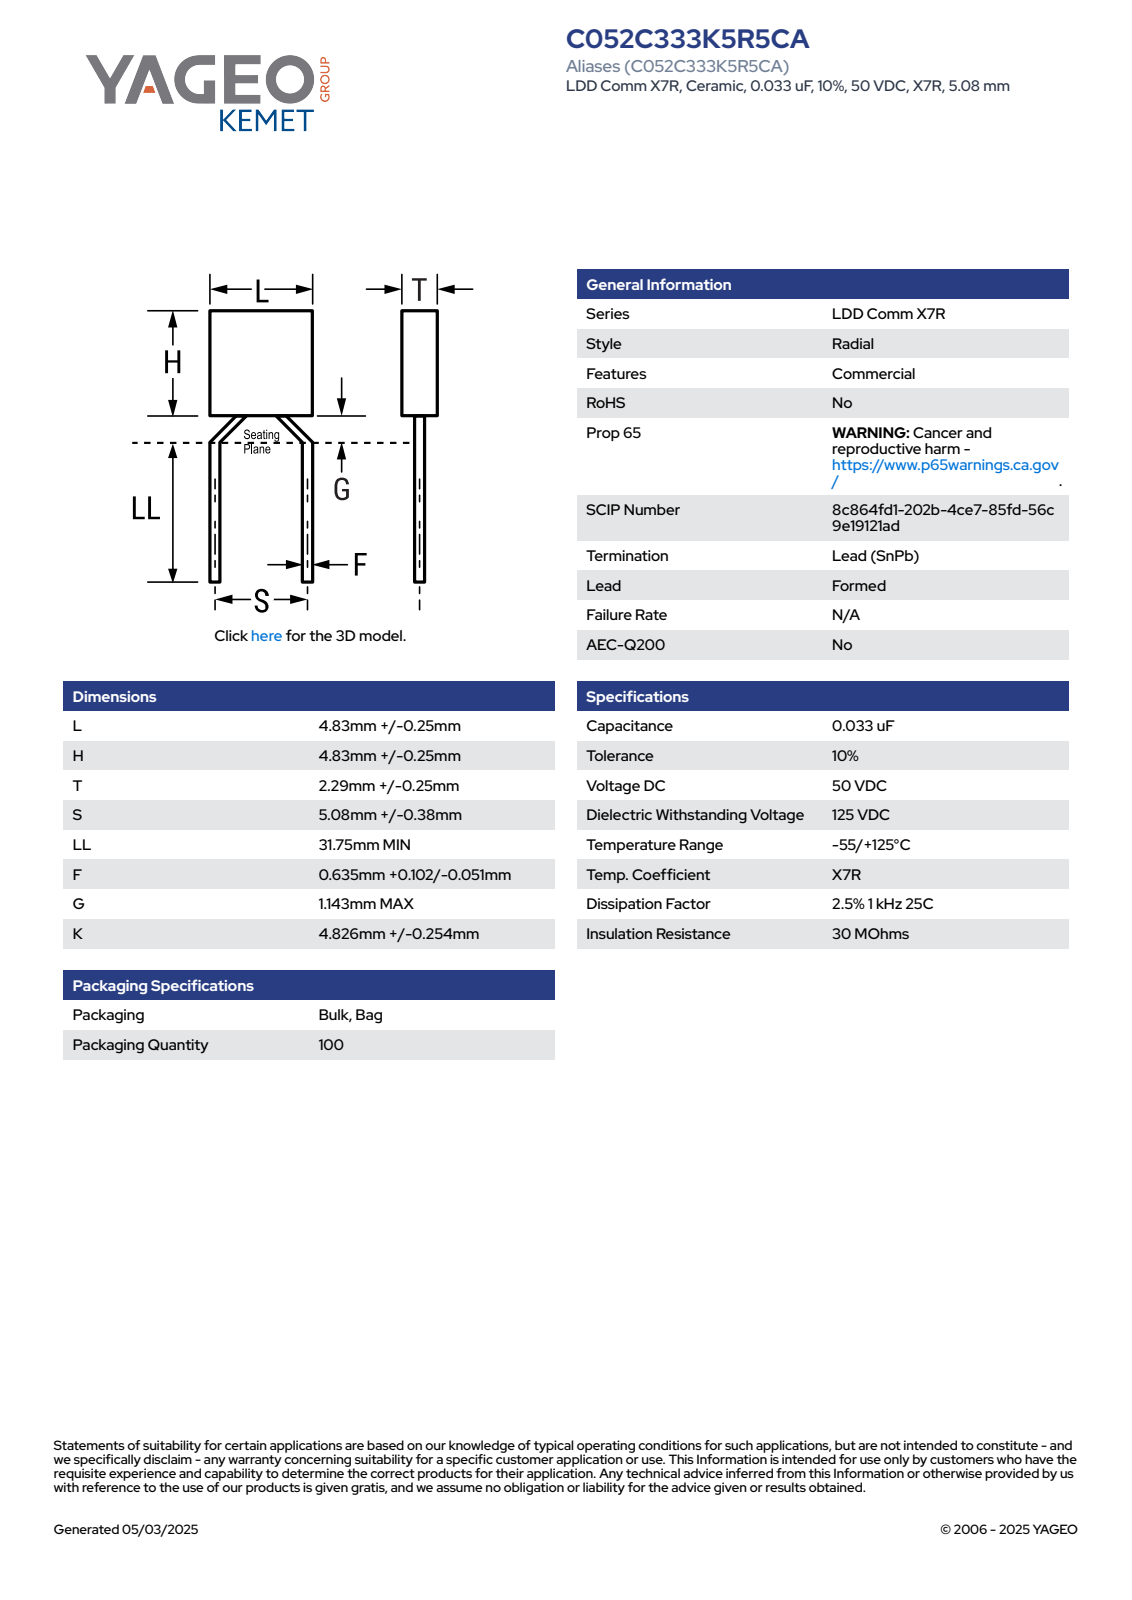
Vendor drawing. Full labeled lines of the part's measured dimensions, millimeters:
Part name (STEP PRODUCT): CCR_RMHS_C052_L5.08H5.08T2.54S5.08LL31.75F0.737G1.143
STEP written by: SolidWorks 2014 (AUTOMOTIVE_DESIGN)
Units: millimetres
Bodies: 4 solids, 73 faces (65 planar, 4 cylindrical, 4 other)
Overall size (bounding box): 37.97 × 5.82 × 2.54
Volume: 94 mm³ · Surface area: 260 mm²
Round bosses / shafts (diameter × count): ⌀0.74 ×2
Main face-to-face distances: 2.54, 5.08, 32.89, 37.97, 35.83, 2.94, 2.14, 35.02, 2.13, 0.81
